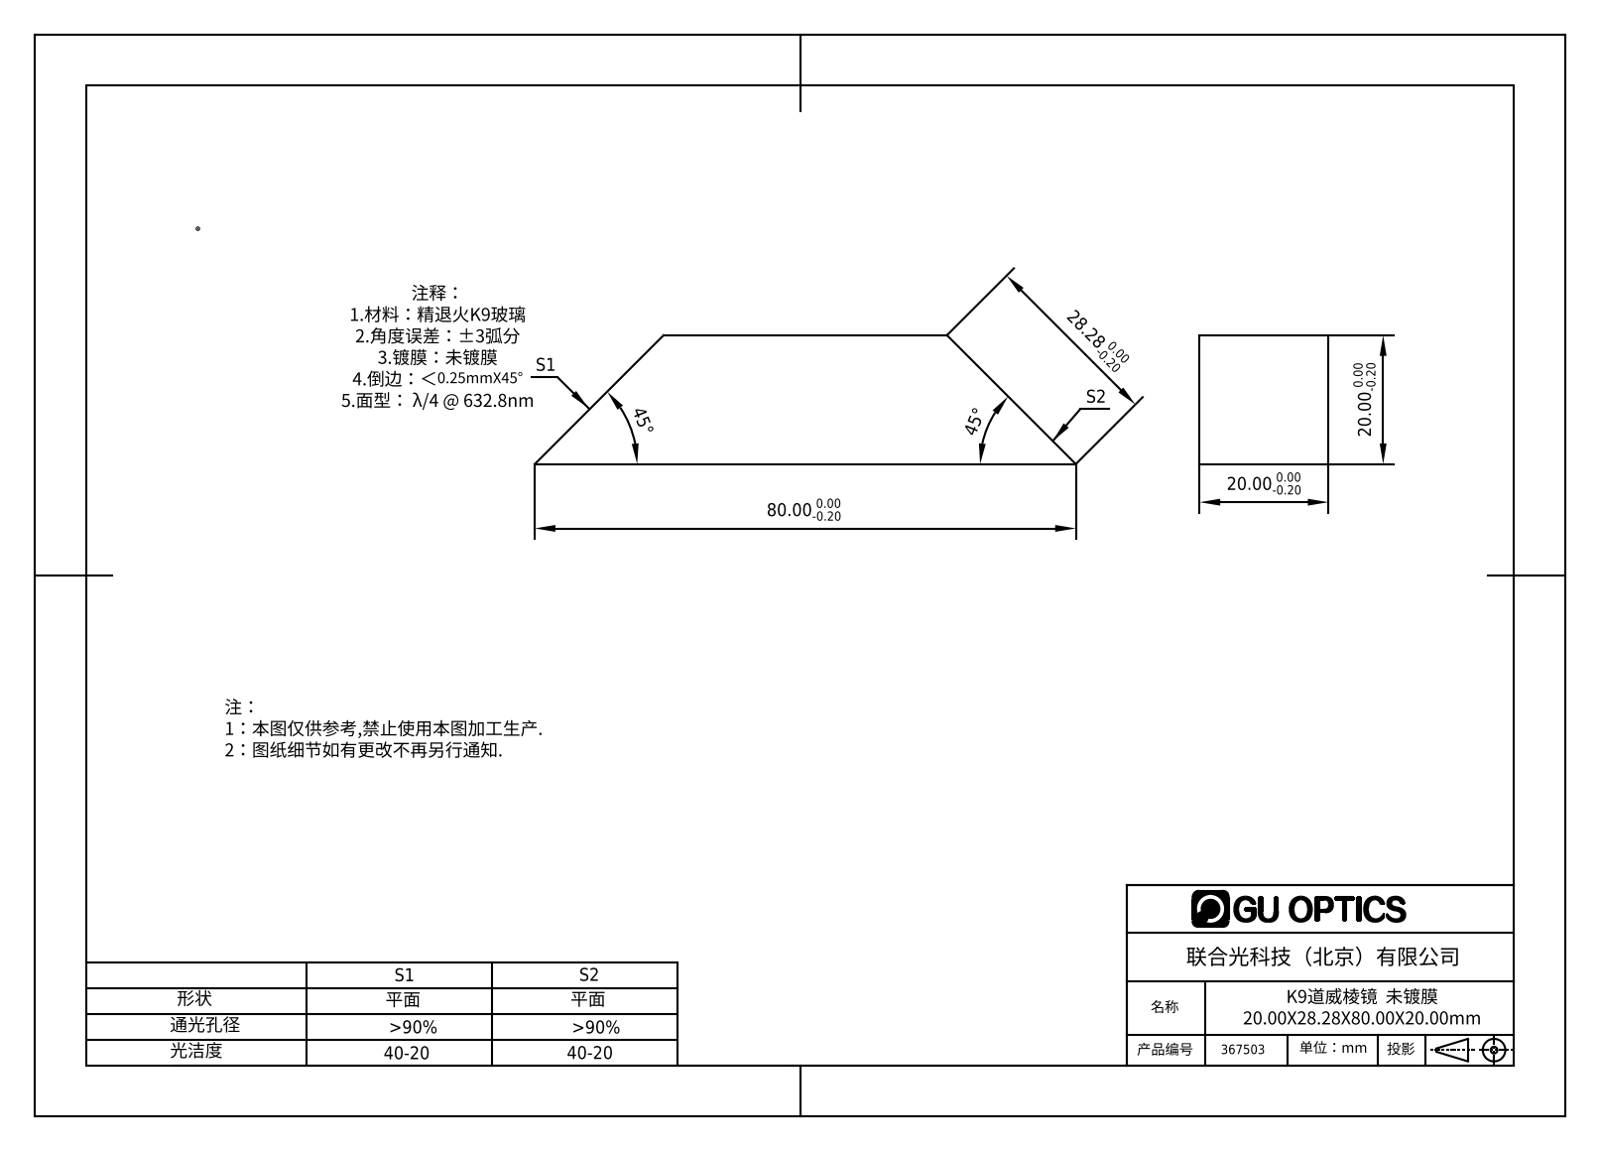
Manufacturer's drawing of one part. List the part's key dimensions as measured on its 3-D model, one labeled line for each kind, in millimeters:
Part name (STEP PRODUCT): 367503
STEP written by: SolidWorks 2020 (CONFIG_CONTROL_DESIGN)
Units: millimetres
Bodies: 1 solid, 6 faces (6 planar, 0 cylindrical, 0 other)
Overall size (bounding box): 84 × 20 × 20
Volume: 25 600 mm³ · Surface area: 6 251 mm²
Main face-to-face distances: 20
